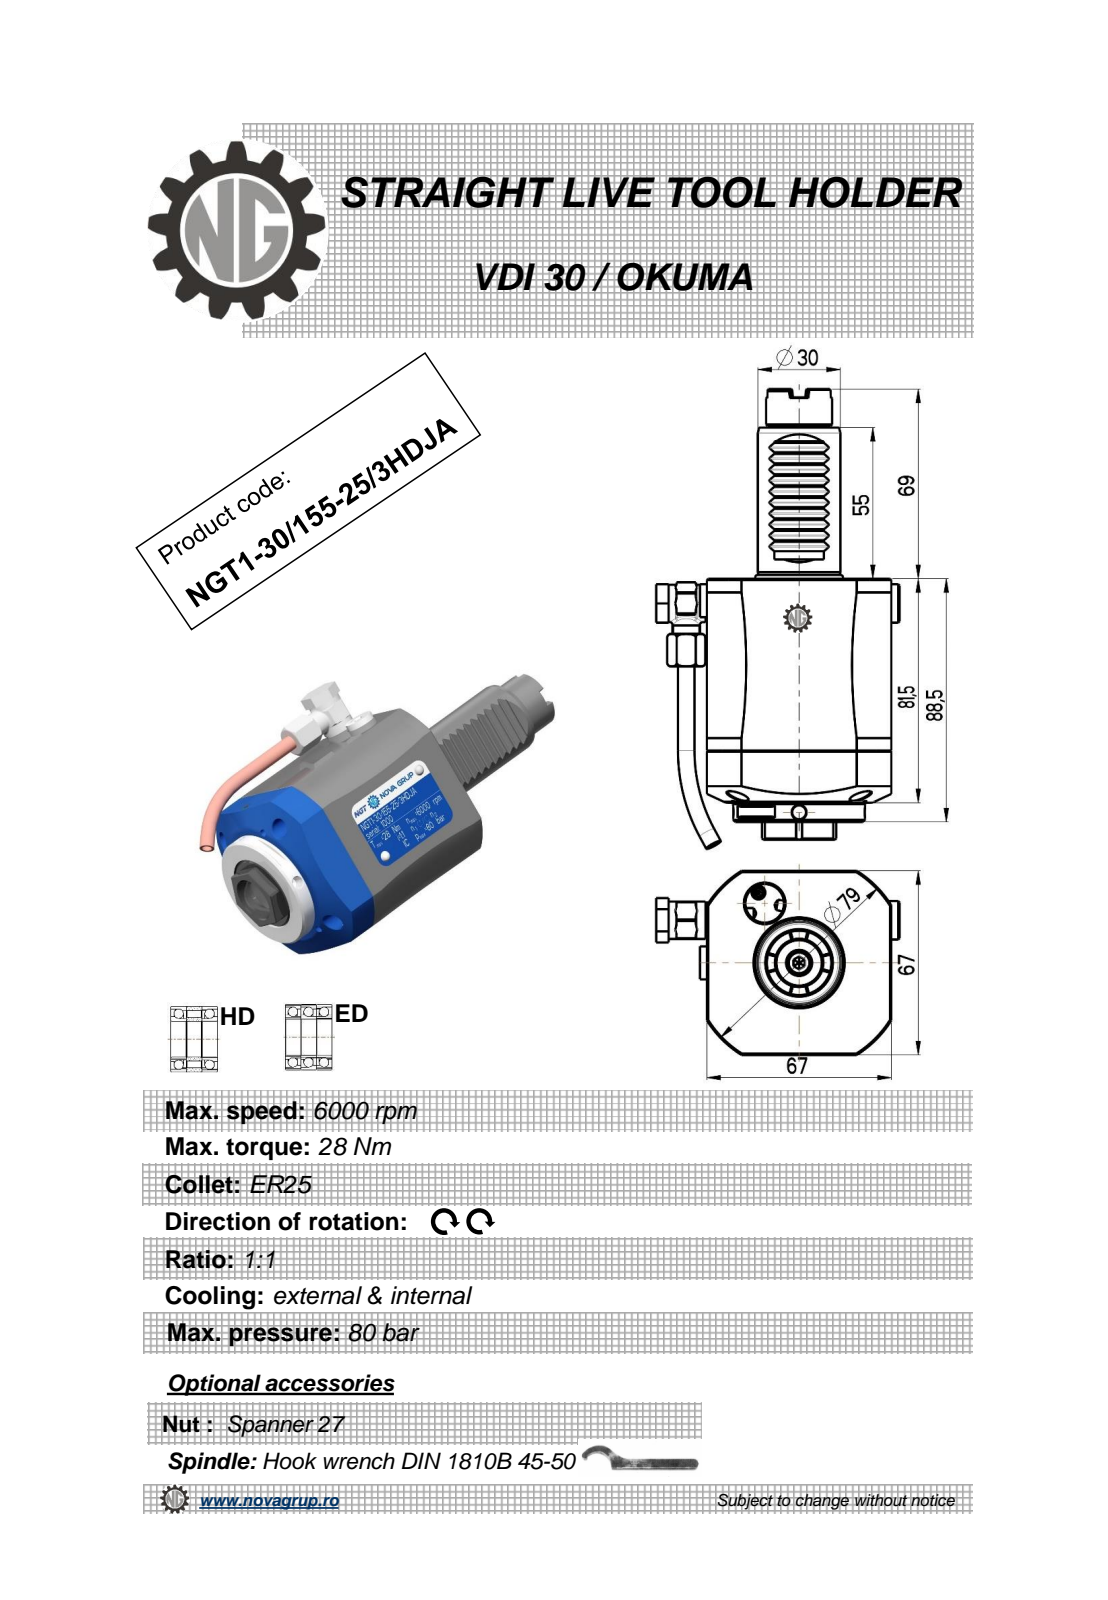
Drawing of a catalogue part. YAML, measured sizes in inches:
part_name: "NGT1_30_155_25_3HDJA"
step_written_by: "PRO/ENGINEER BY PARAMETRIC TECHNOLOGY CORPORATION, 2010280 (CONFIG_CONTROL_DESIGN)"
units: inches
bodies: {solids: 2, faces: 417, planar: 163, cylindrical: 103, other: 151}
overall_size: [6.588, 3.48, 2.638]
volume: 24.09
surface_area: 66.47
round_holes:
  - {diameter: 0.157, count: 3}
  - {diameter: 0.197, count: 2}
  - {diameter: 0.118, count: 1}
  - {diameter: 0.236, count: 1}
  - {diameter: 0.244, count: 1}
  - {diameter: 0.354, count: 1}
  - {diameter: 0.394, count: 1}
  - {diameter: 0.433, count: 1}
  - {diameter: 0.669, count: 1}
  - {diameter: 0.709, count: 1}
  - {diameter: 1.043, count: 1}
round_bosses_or_shafts:
  - {diameter: 1.89, count: 1}
  - {diameter: 1.181, count: 1}
  - {diameter: 0.945, count: 1}
  - {diameter: 0.551, count: 1}
  - {diameter: 0.535, count: 1}
  - {diameter: 0.512, count: 1}
  - {diameter: 0.472, count: 1}
  - {diameter: 0.394, count: 1}
partial_cylinders:
  - {radius: 0.012, count: 10}
  - {radius: 0.016, count: 6}
  - {radius: 0.02, count: 4}
  - {radius: 0.303, count: 1}
  - {radius: 1.555, count: 1}
face_to_face_distances: [2.638, 3.484, 0.276, 3.209, 0.111, 0.223, 2.165, 0.557, 5.65, 5.374]
hole_center_spacings: [0.016, 1.726, 1.741, 3.054]
